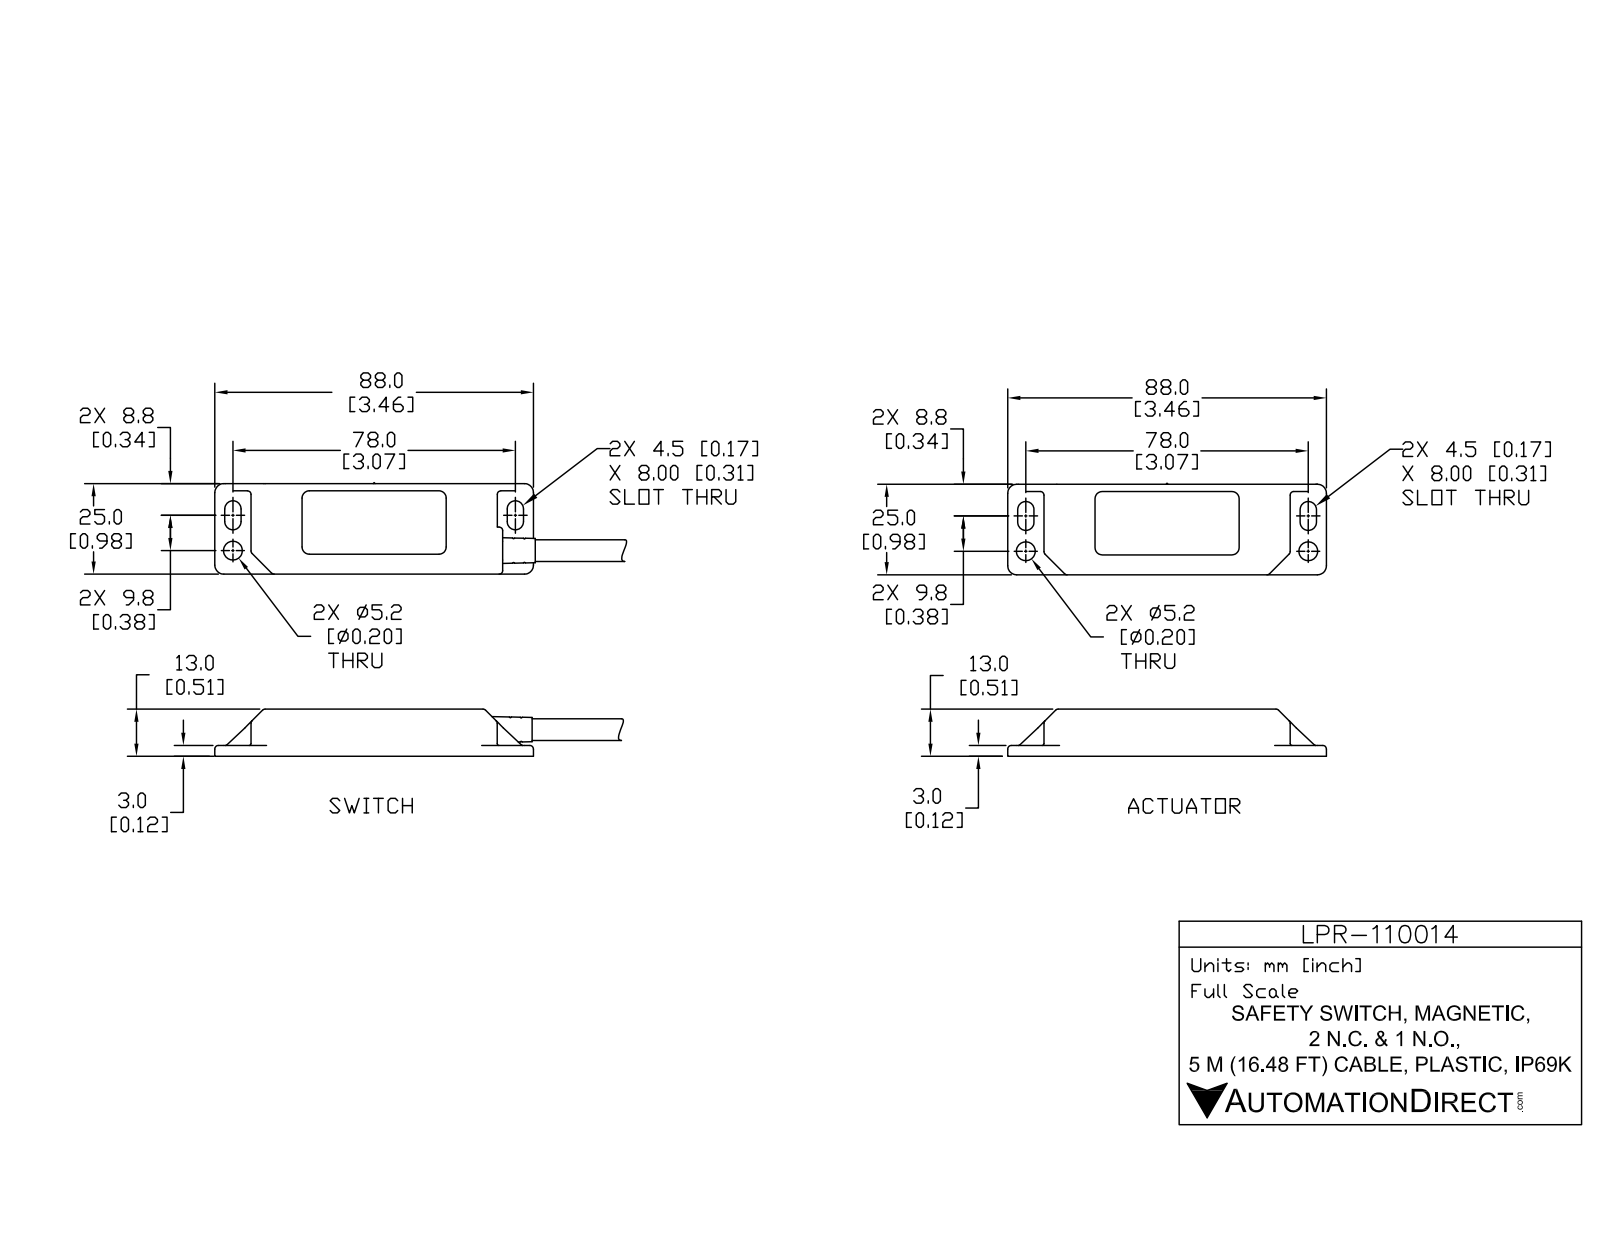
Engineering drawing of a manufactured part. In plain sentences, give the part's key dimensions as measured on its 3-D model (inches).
The part is named "LPR-110014; LPR-110014_2; LPR-110014_1". Its 3-D file was written by "SolidWorks 2017 (AUTOMOTIVE_DESIGN)". It is 11 solids with 1058 faces: 401 planar, 303 cylindrical and 354 other. Overall it measures 8.849 by 1.992 by 0.543 inches. Its volume is 1.638 cubic inches and its surface area 46.88 square inches. Round holes: 4 of diameter 0.197, 4 of diameter 0.205, 1 of diameter 0.119, 1 of diameter 0.173, 1 of diameter 0.213, 1 of diameter 0.232, 1 of diameter 0.276. Round bosses or shafts: 4 of diameter 0.079, 2 of diameter 0.193, 2 of diameter 0.091, 1 of diameter 0.339, 1 of diameter 0.299, 1 of diameter 0.28, 1 of diameter 0.236, 1 of diameter 0.209. Partial cylindrical surfaces (rounded edges, fillets, slot ends): 116 of radius 0.02, 49 of radius 0.039, 10 of radius 0.079, 8 of radius 0.089, 8 of radius 0.098, 6 of radius 0.012, 1 of radius 0.189. The main face-to-face distances are 0.067, 0.441, 0.079, 0.374, 0.059, 0.071, 0.508, 0.445, 0.512, 0.988. The hole center spacings are 0.748, 1.097, 1.19, 1.275, 1.48, 1.571, 1.784, 1.895.
